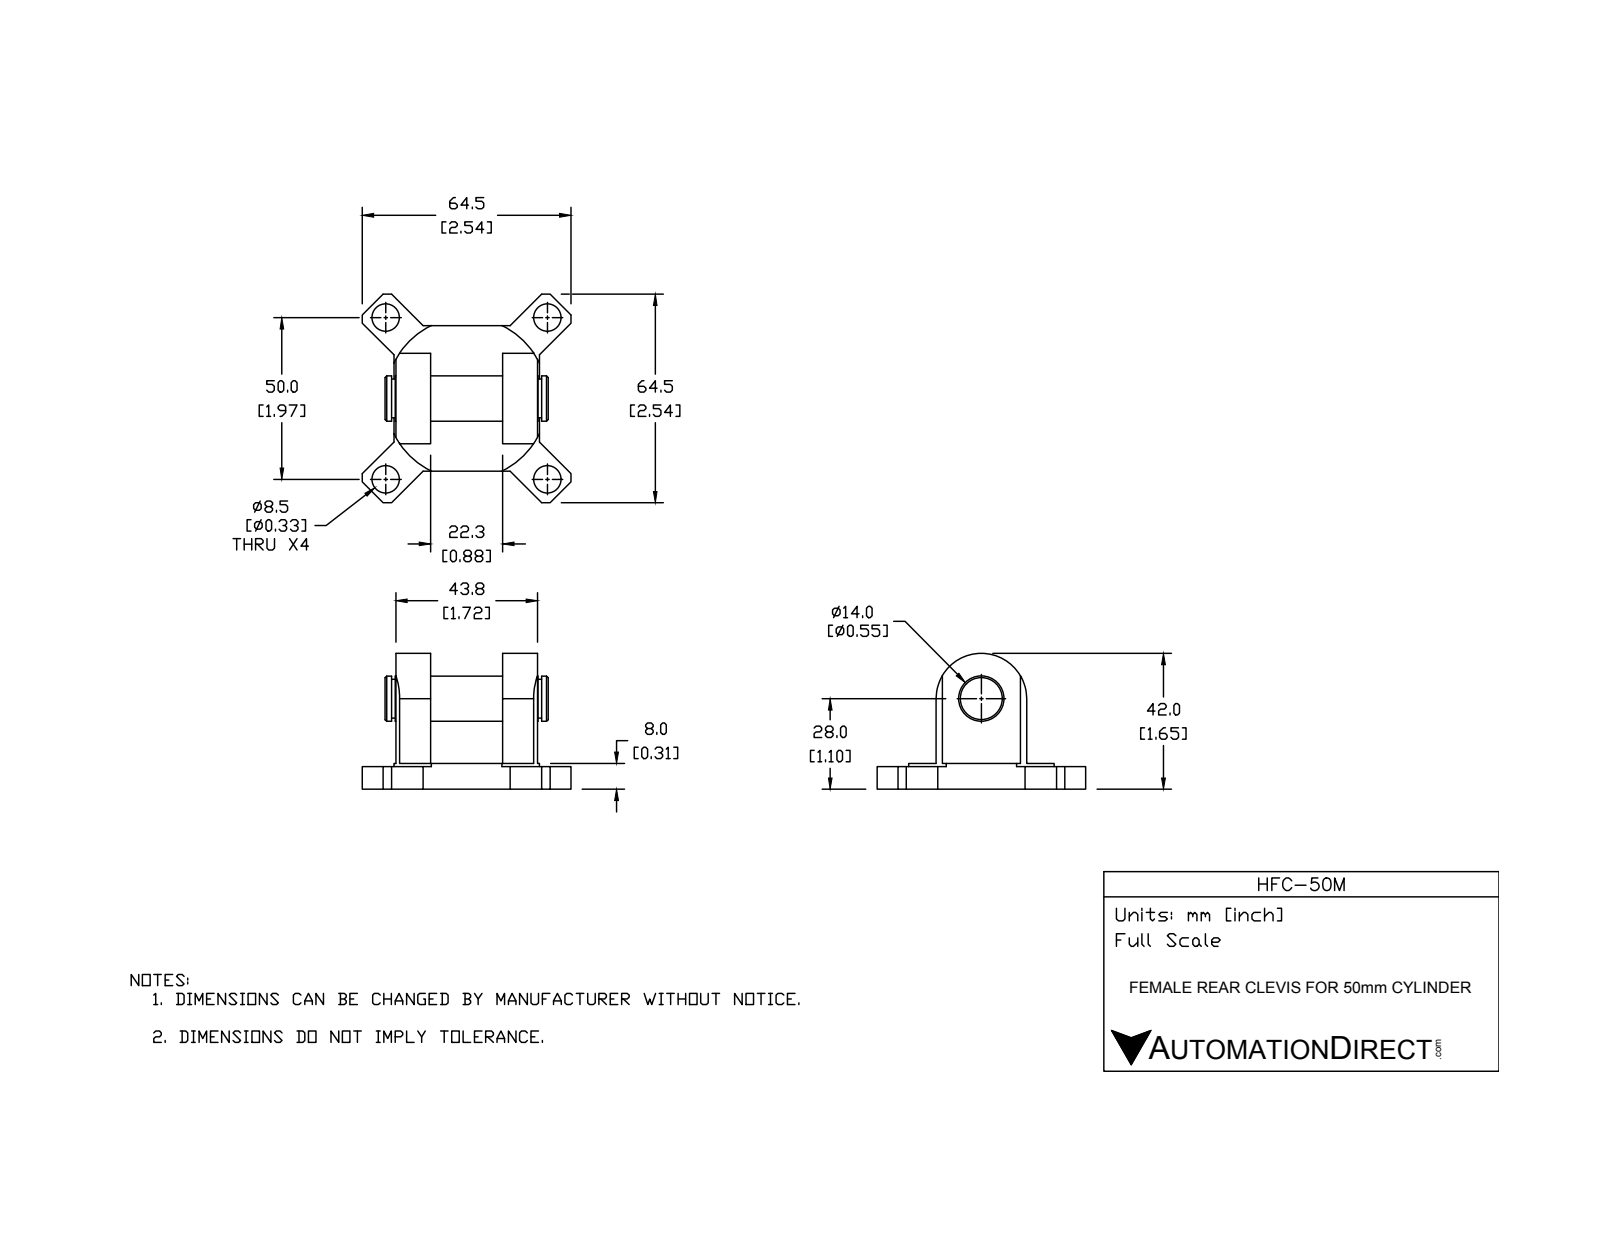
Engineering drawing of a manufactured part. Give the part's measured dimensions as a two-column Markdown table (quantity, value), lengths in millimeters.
| quantity | value |
| --- | --- |
| part name | HFC-50M |
| STEP written by | SolidWorks 2015 (CONFIG_CONTROL_DESIGN) |
| units | millimeters |
| bodies | 2 solids, 78 faces (46 planar, 28 cylindrical, 4 other) |
| overall size | 64.5 × 64.5 × 42 |
| volume | 41 644 mm³ |
| surface area | 15 236 mm² |
| round holes (diameter × count) | 8.5 × 4 |
| round bosses / shafts (diameter × count) | 14 × 1, 12 × 1 |
| partial cylindrical surfaces (radius × count) | 14 × 1, 25 × 1 |
| main face-to-face distances | 10.75, 33.05, 8, 22.3, 43.8, 7, 1, 0.6, 11.35, 33.65 |
| hole center spacings | 50, 70.71 |
